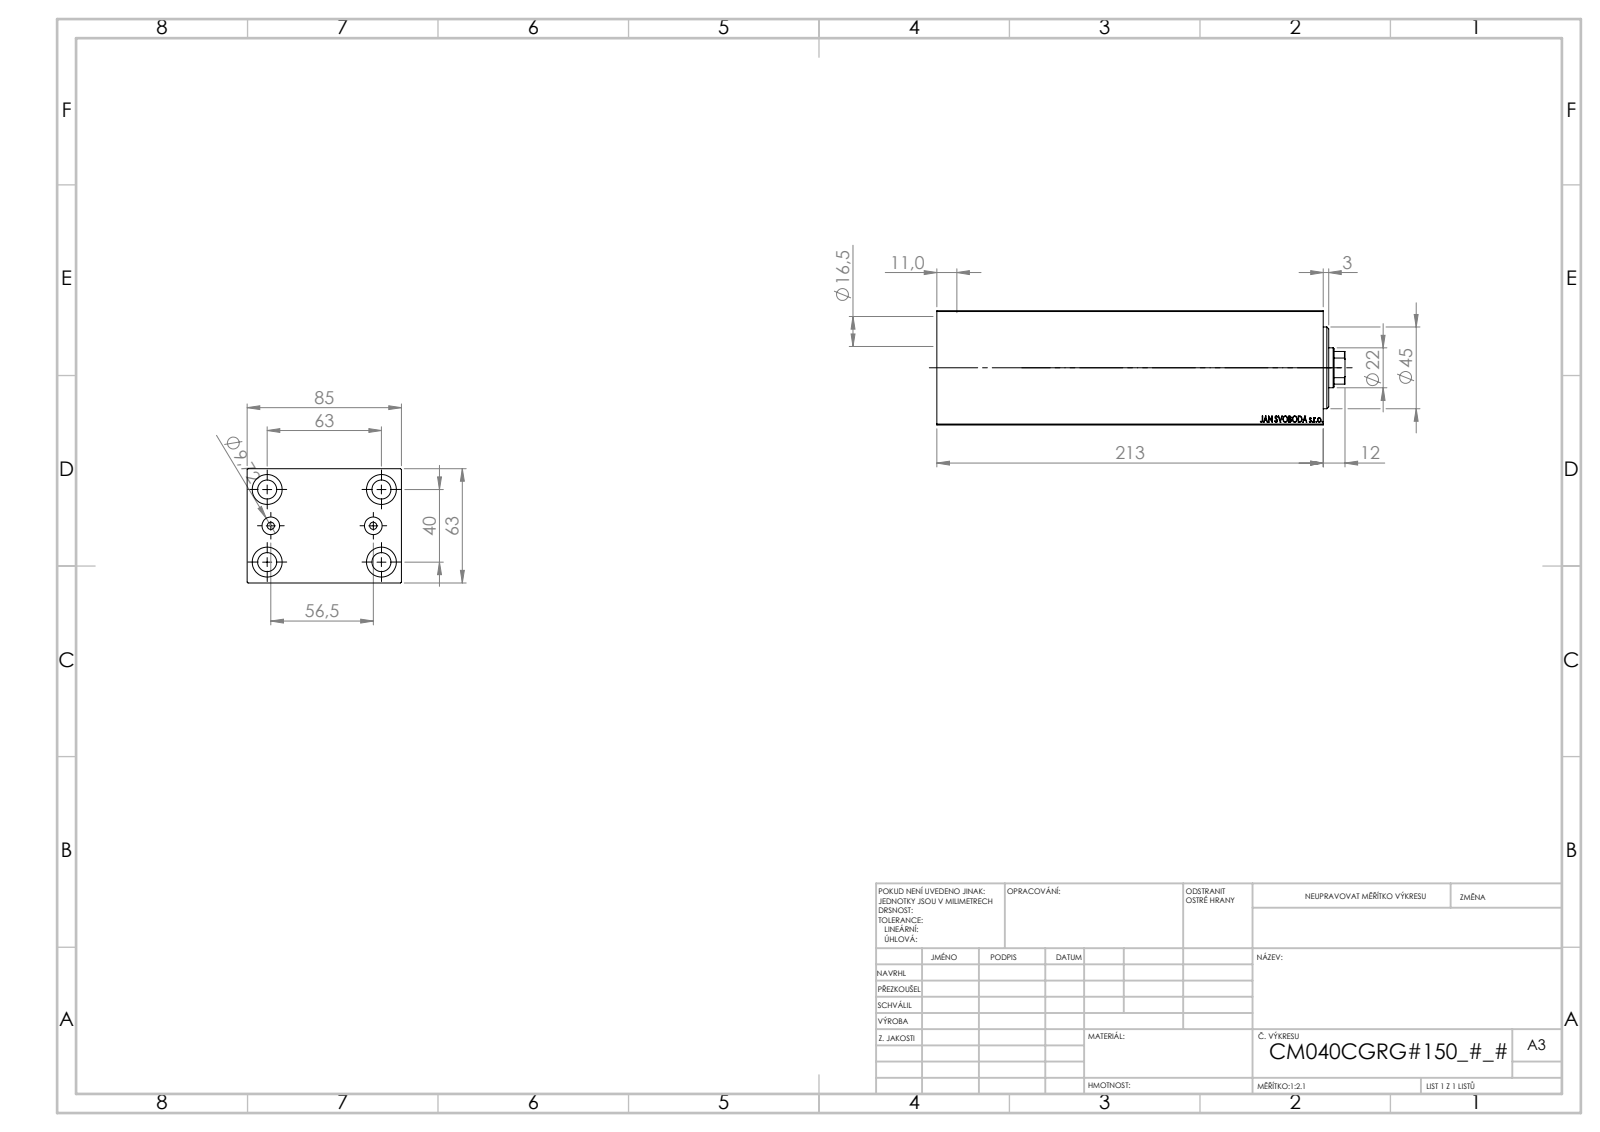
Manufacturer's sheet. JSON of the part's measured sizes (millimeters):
{"part_name": "V450CM_VC_B; V450CM_C_VCP; V450CM_C_Body", "step_written_by": "SolidWorks 2019 (CONFIG_CONTROL_DESIGN)", "units": "millimeters", "bodies": {"solids": 3, "faces": 858, "planar": 408, "cylindrical": 56, "other": 394}, "overall_size": [225, 85, 63], "volume_mm3": 922471, "surface_area_mm2": 159203, "round_holes": [[10.5, 4], [16.5, 4], [4, 2], [9.72, 2], [12.5, 1], [22, 1], [25.5, 1], [40, 1], [42, 1], [45, 1]], "partial_cylinders_radius": [[10.5, 1]], "face_to_face_distances": [63, 85, 12, 201, 213, 1, 189, 11, 202, 190], "hole_center_spacings": [37.31, 20.1, 20.5, 40, 61.82, 63, 64.2, 74.63]}
